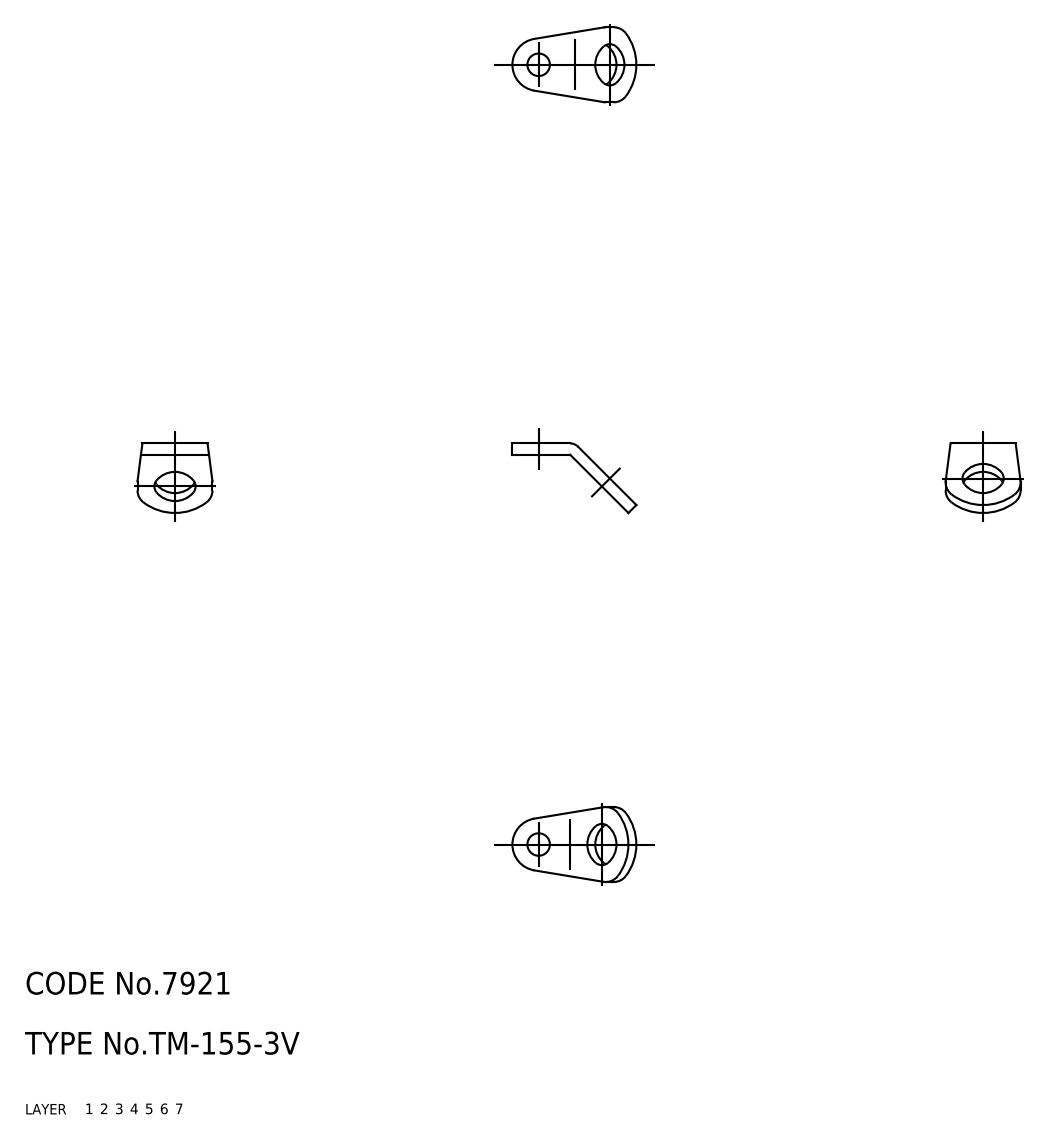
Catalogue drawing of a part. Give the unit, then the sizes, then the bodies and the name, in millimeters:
Units: millimetres
Overall size (bounding box): 16.53 × 10 × 9.28
Volume: 181 mm³ · Surface area: 355 mm²
Bodies: 1 solid, 21 faces (0 planar, 0 cylindrical, 21 other)
Part name (STEP PRODUCT): terminal
STEP written by: CADfix (AUTOMOTIVE_DESIGN)
